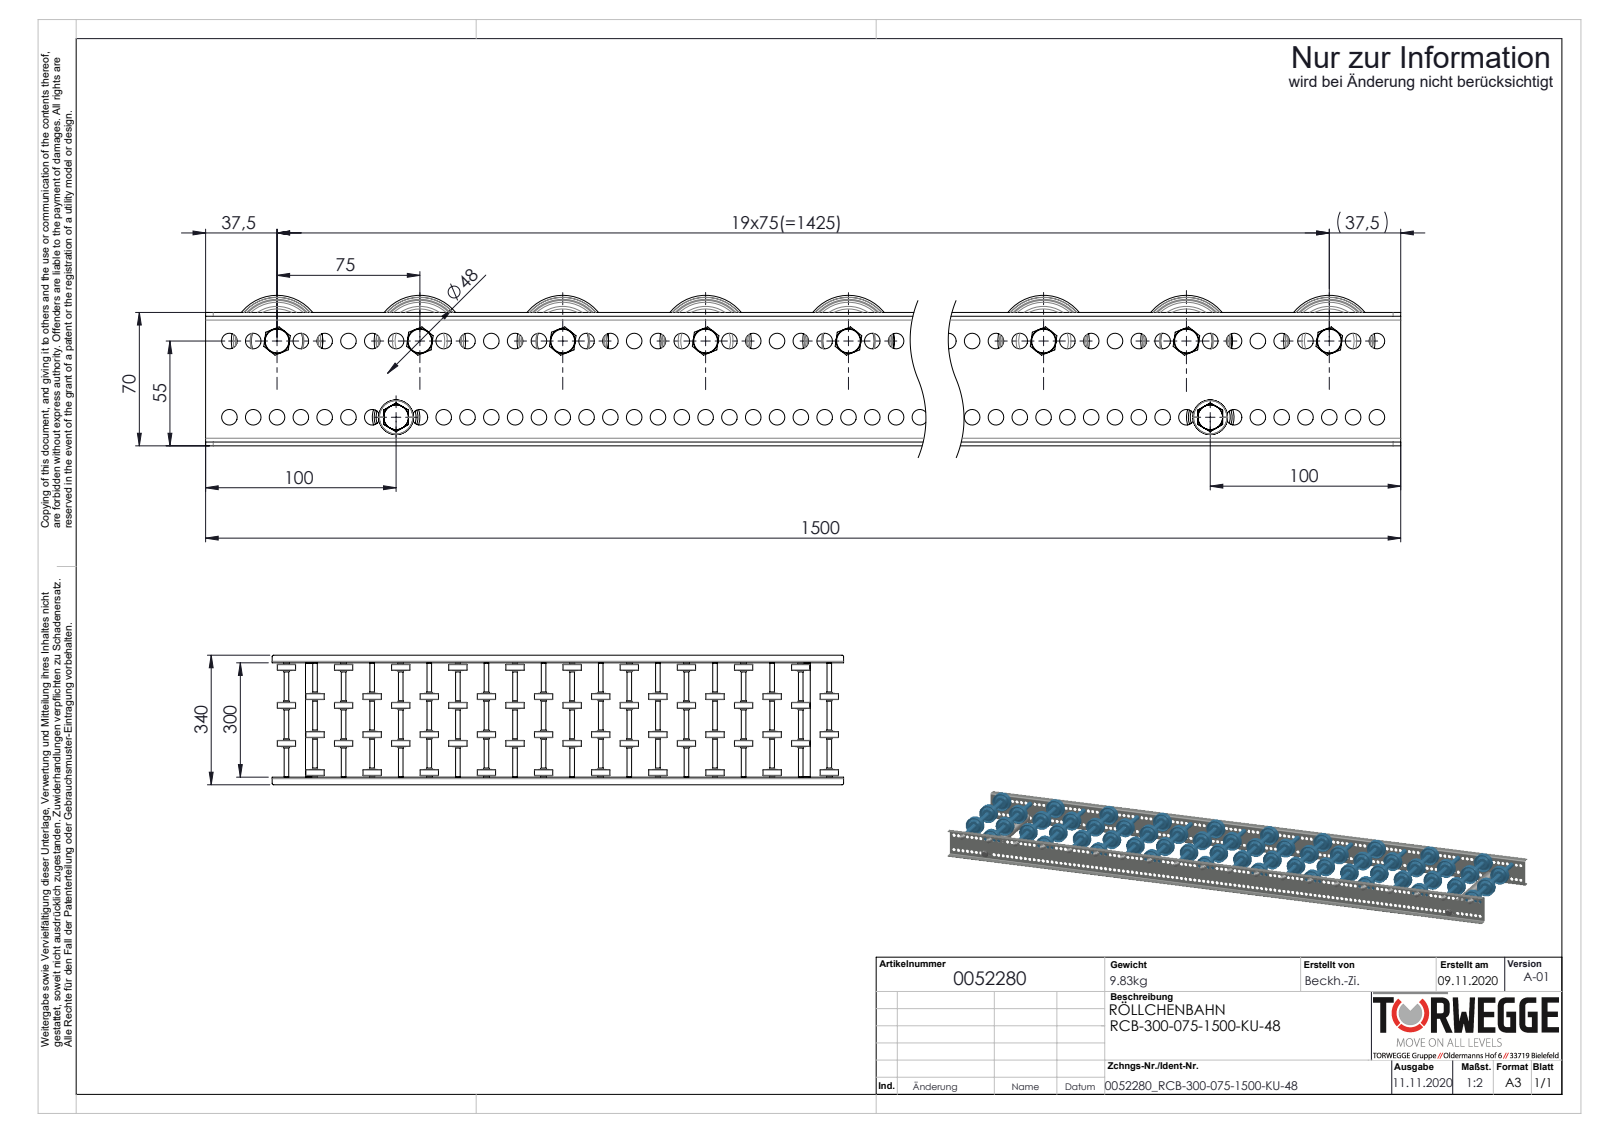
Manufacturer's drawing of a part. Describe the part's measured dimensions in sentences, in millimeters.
The part is named "Traversen_KFG_L300; 0011532_2300-48-8; S106837_Gewindestange-M8-KFG_L320; 0052280 (+5 more)". Its 3-D file was written by "SolidWorks 2020 (AUTOMOTIVE_DESIGN)". It is 192 solids with 7012 faces: 1260 planar, 2528 cylindrical and 3224 other. Overall it measures 1500 by 340 by 79 millimeters. Its volume is 2 375 000 cubic millimeters and its surface area 1 797 000 square millimeters. Round holes: 238 of diameter 8.2, 20 of diameter 6.65, 20 of diameter 9.65, 20 of diameter 13.7, 2 of diameter 6.8, 2 of diameter 21. Round bosses or shafts: 22 of diameter 8, 20 of diameter 48, 20 of diameter 27, 20 of diameter 12.7, 20 of diameter 12.5, 20 of diameter 12, 2 of diameter 25. Partial cylindrical surfaces (rounded edges, fillets, slot ends): 8 of radius 4, 4 of radius 2. The main face-to-face distances are 2, 302, 68, 304, 300, 70, 66, 99.8, 16.3, 76.1. The hole center spacings are 12.5, 25, 37.5, 50, 62.5, 75, 87.5, 100.
